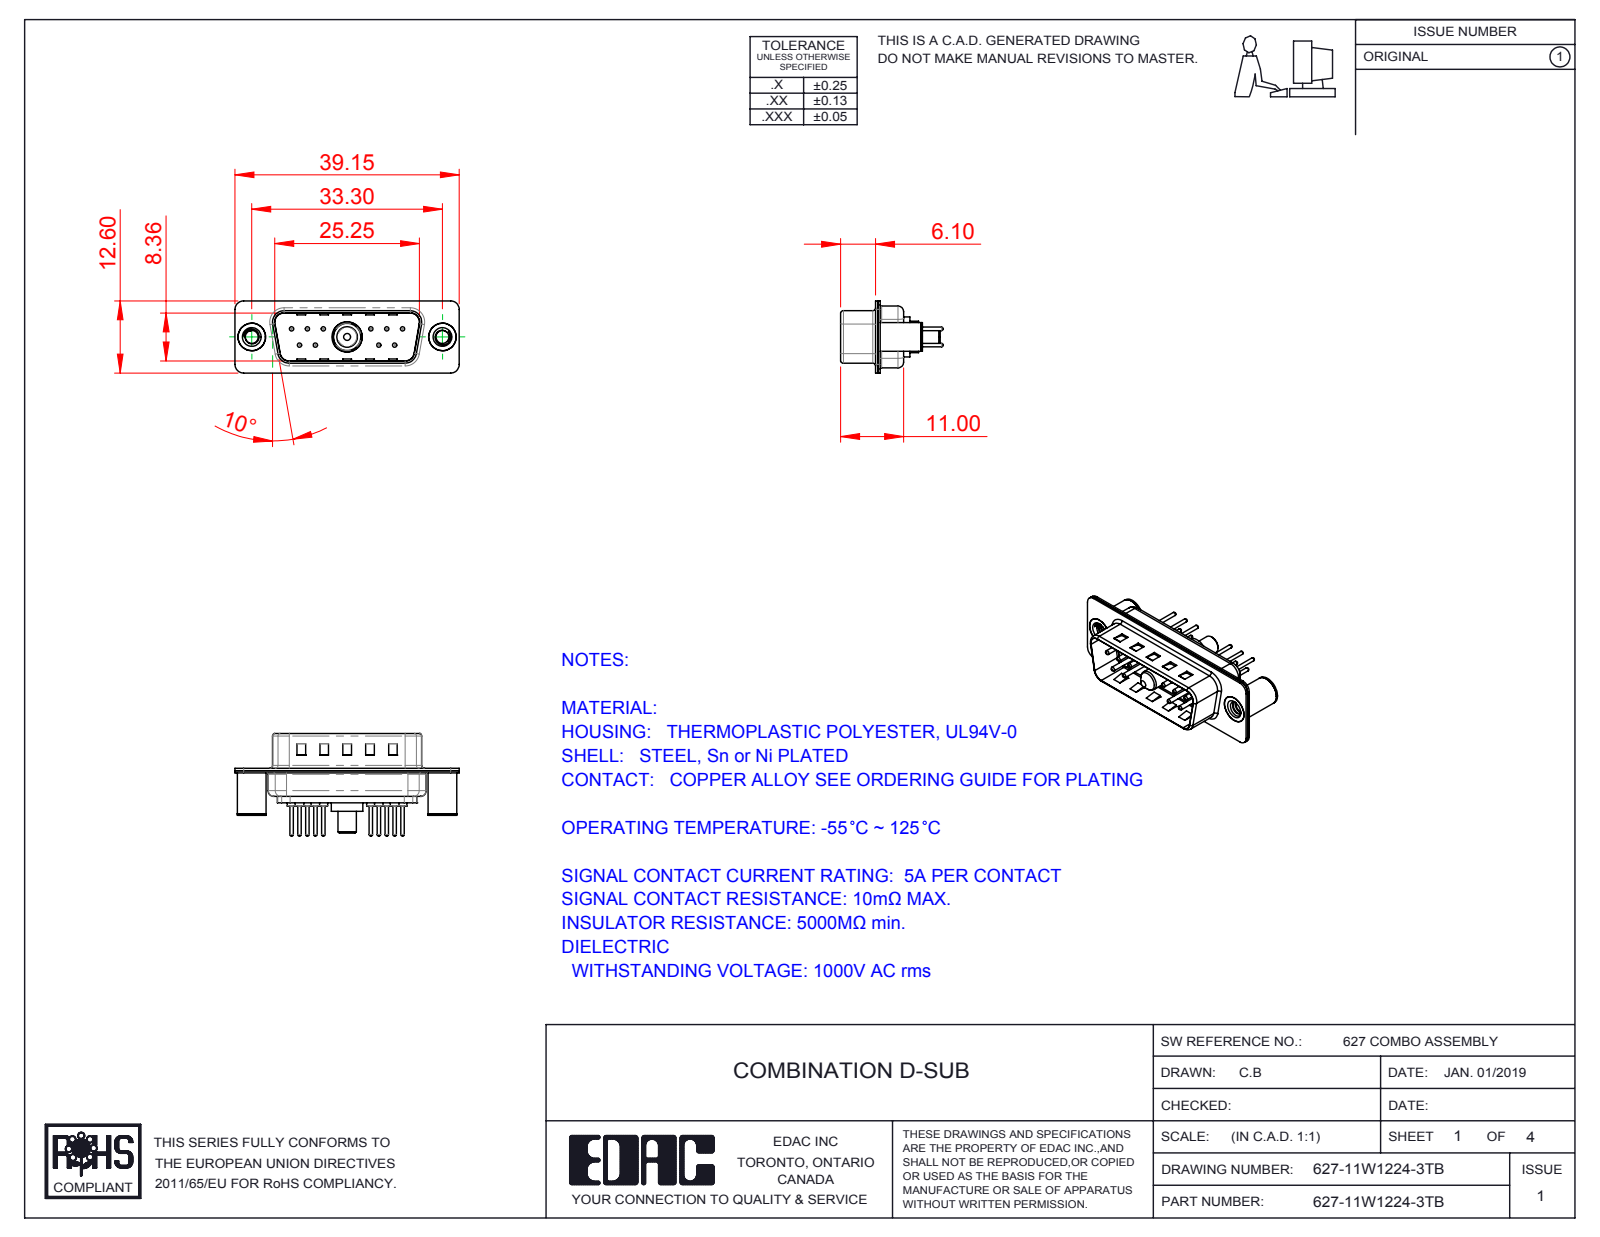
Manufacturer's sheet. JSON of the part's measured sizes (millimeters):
{"part_name": "627Combo Threaded Board Spacer_3; 627Combo Threaded Board Spacer_B; 627Combo Shell Rear_15 Contacts; 627Combo Shell Front_15 Contacts (+5 more)", "step_written_by": "SolidWorks 2016 (CONFIG_CONTROL_DESIGN)", "units": "millimeters", "bodies": {"solids": 17, "faces": 801, "planar": 228, "cylindrical": 324, "other": 249}, "overall_size": [39.15, 17.9, 12.6], "volume_mm3": 2043, "surface_area_mm2": 5050, "round_holes": [[0.75, 10], [1.6, 10], [2, 10], [2.26, 2], [3.26, 2], [4, 2], [4.8, 2], [4.85, 1], [5.3, 1]], "round_bosses_or_shafts": [[1.5, 10], [0.6, 10], [5, 2], [4.9, 2], [5.5, 1], [5.2, 1], [4.75, 1], [3.75, 1]], "partial_cylinders_radius": [[1.5, 20], [2, 12], [0.5, 8], [1.6, 8], [1, 7], [0.25, 4], [0.6, 4], [0.65, 4]], "face_to_face_distances": [0.4, 0.82, 9.58, 8.76, 0.8, 1.5, 5.6, 5.2, 6, 1.22], "hole_center_spacings": [3.16, 2.77, 13.85, 11.08, 16.62, 5.03, 5.04, 5.54]}
